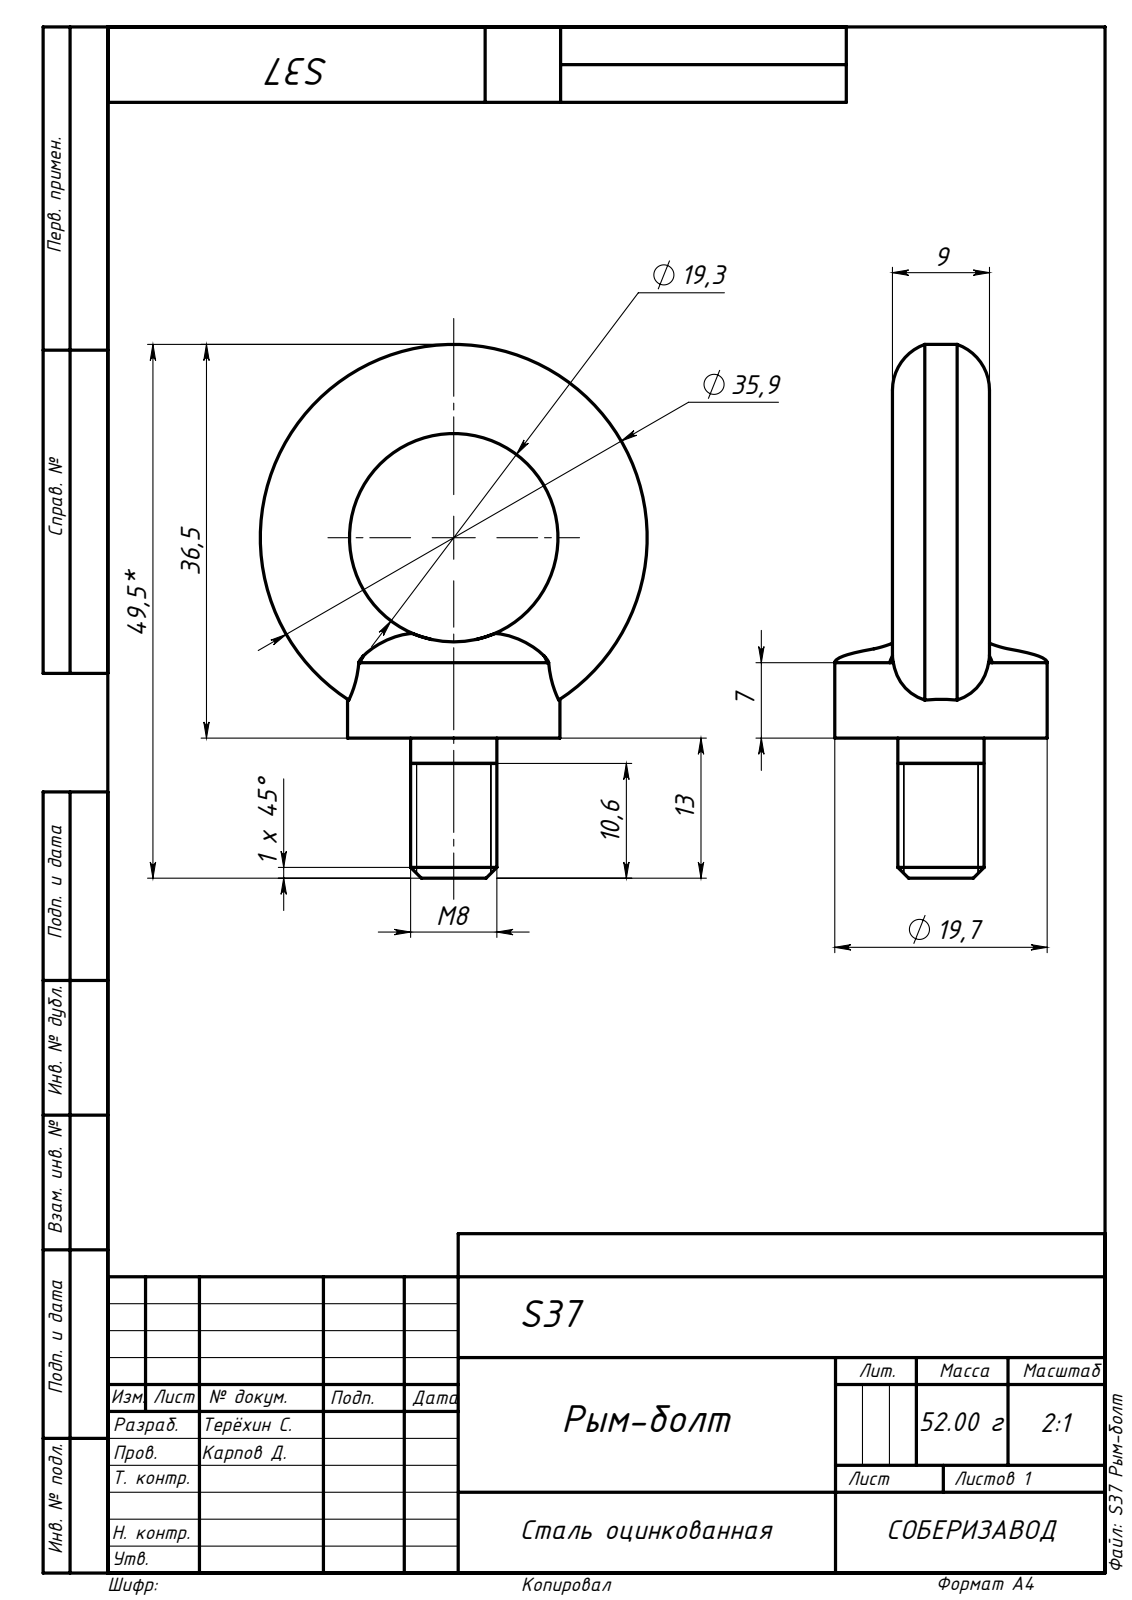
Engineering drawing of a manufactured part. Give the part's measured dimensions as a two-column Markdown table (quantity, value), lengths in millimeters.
| quantity | value |
| --- | --- |
| part name | S37 Рым-болт |
| STEP written by | SolidWorks 2020 (AUTOMOTIVE_DESIGN) |
| units | millimeters |
| bodies | 1 solid, 29 faces (2 planar, 9 cylindrical, 18 other) |
| overall size | 49.54 × 35.88 × 19.7 |
| volume | 7 499 mm³ |
| surface area | 3 234 mm² |
| round holes (diameter × count) | 19.34 × 1 |
| round bosses / shafts (diameter × count) | 35.89 × 1, 19.7 × 1, 8 × 1 |
| main face-to-face distances | 13 |
